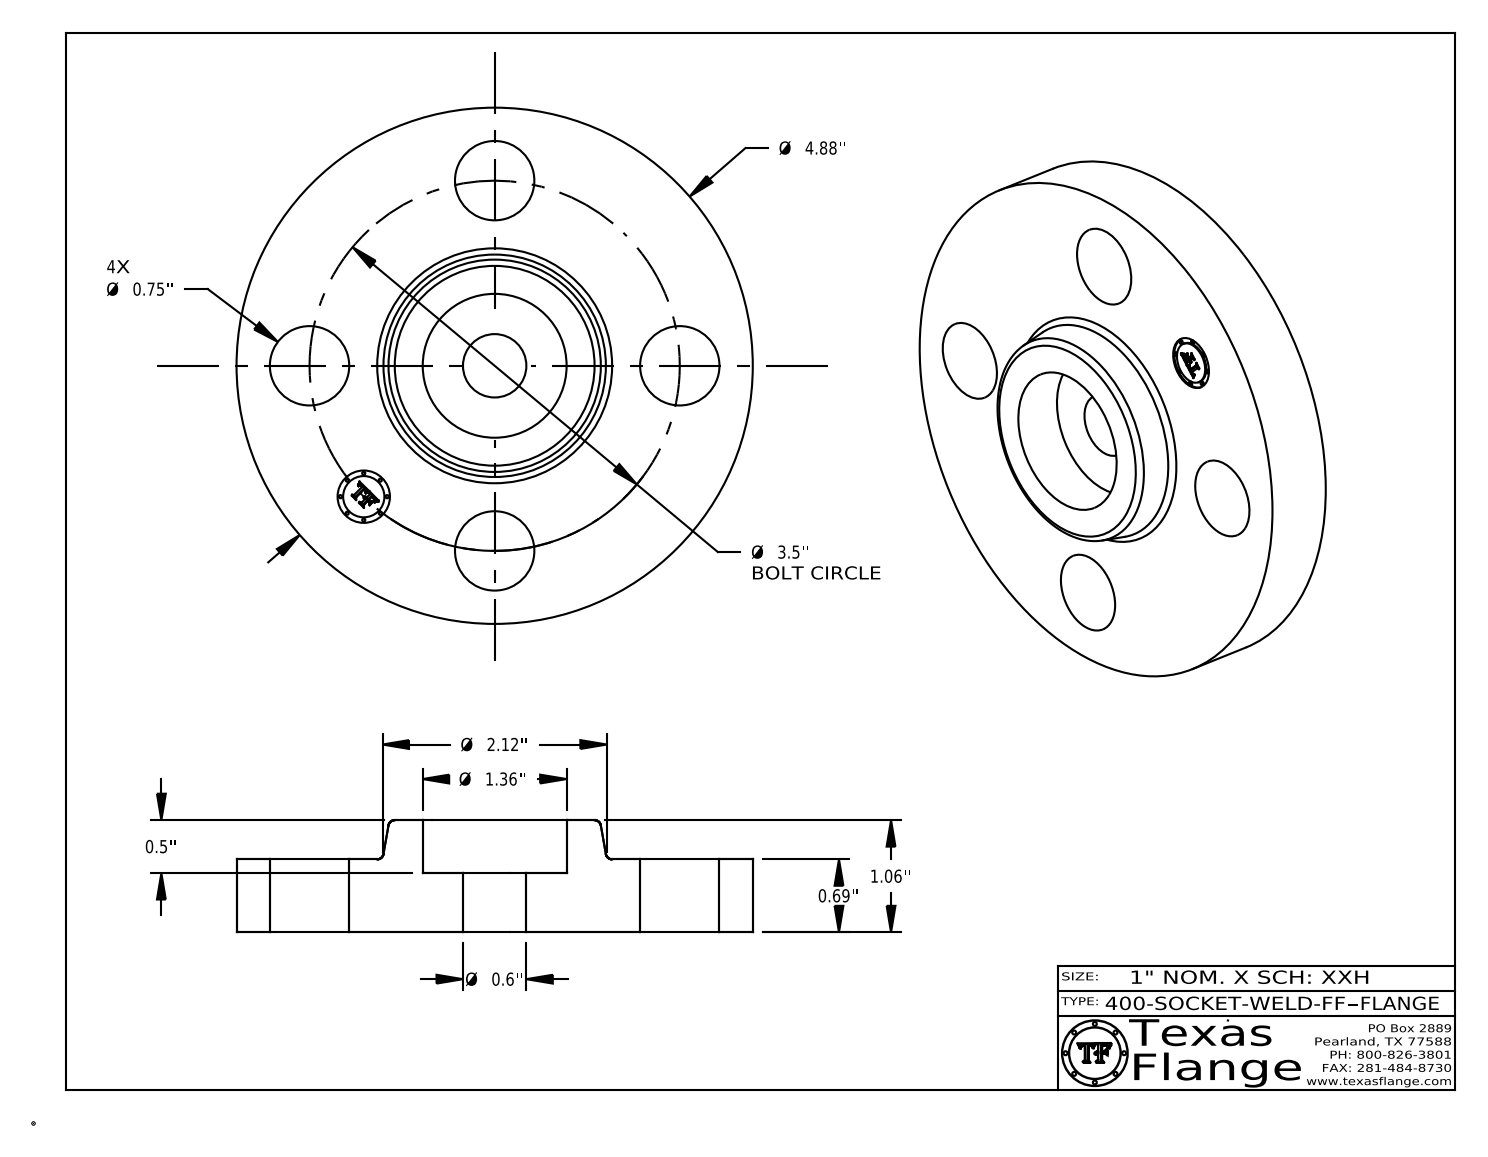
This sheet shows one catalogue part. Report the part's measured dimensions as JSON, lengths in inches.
{"part_name": "400-SOCKET-WELD-FF", "step_written_by": "CATIA V5 STEP AP214 (AUTOMOTIVE_DESIGN)", "units": "inches", "bodies": {"solids": 1, "faces": 409, "planar": 369, "cylindrical": 34, "other": 6}, "overall_size": [4.88, 4.88, 1.06], "volume_in3": 12.03, "surface_area_in2": 55.46, "round_holes": [[0.75, 4], [0.495, 1], [0.599, 1], [1.36, 1]], "round_bosses_or_shafts": [[0.03, 8], [4.88, 1], [0.39, 1]], "face_to_face_distances": [0.69, 1.06, 0.37, 0.56, 0.13, 0.5, 0.015, 0.675, 0.115, 0.385], "hole_center_spacings": [1.75, 2.475, 1.339, 3.233, 3.5]}
